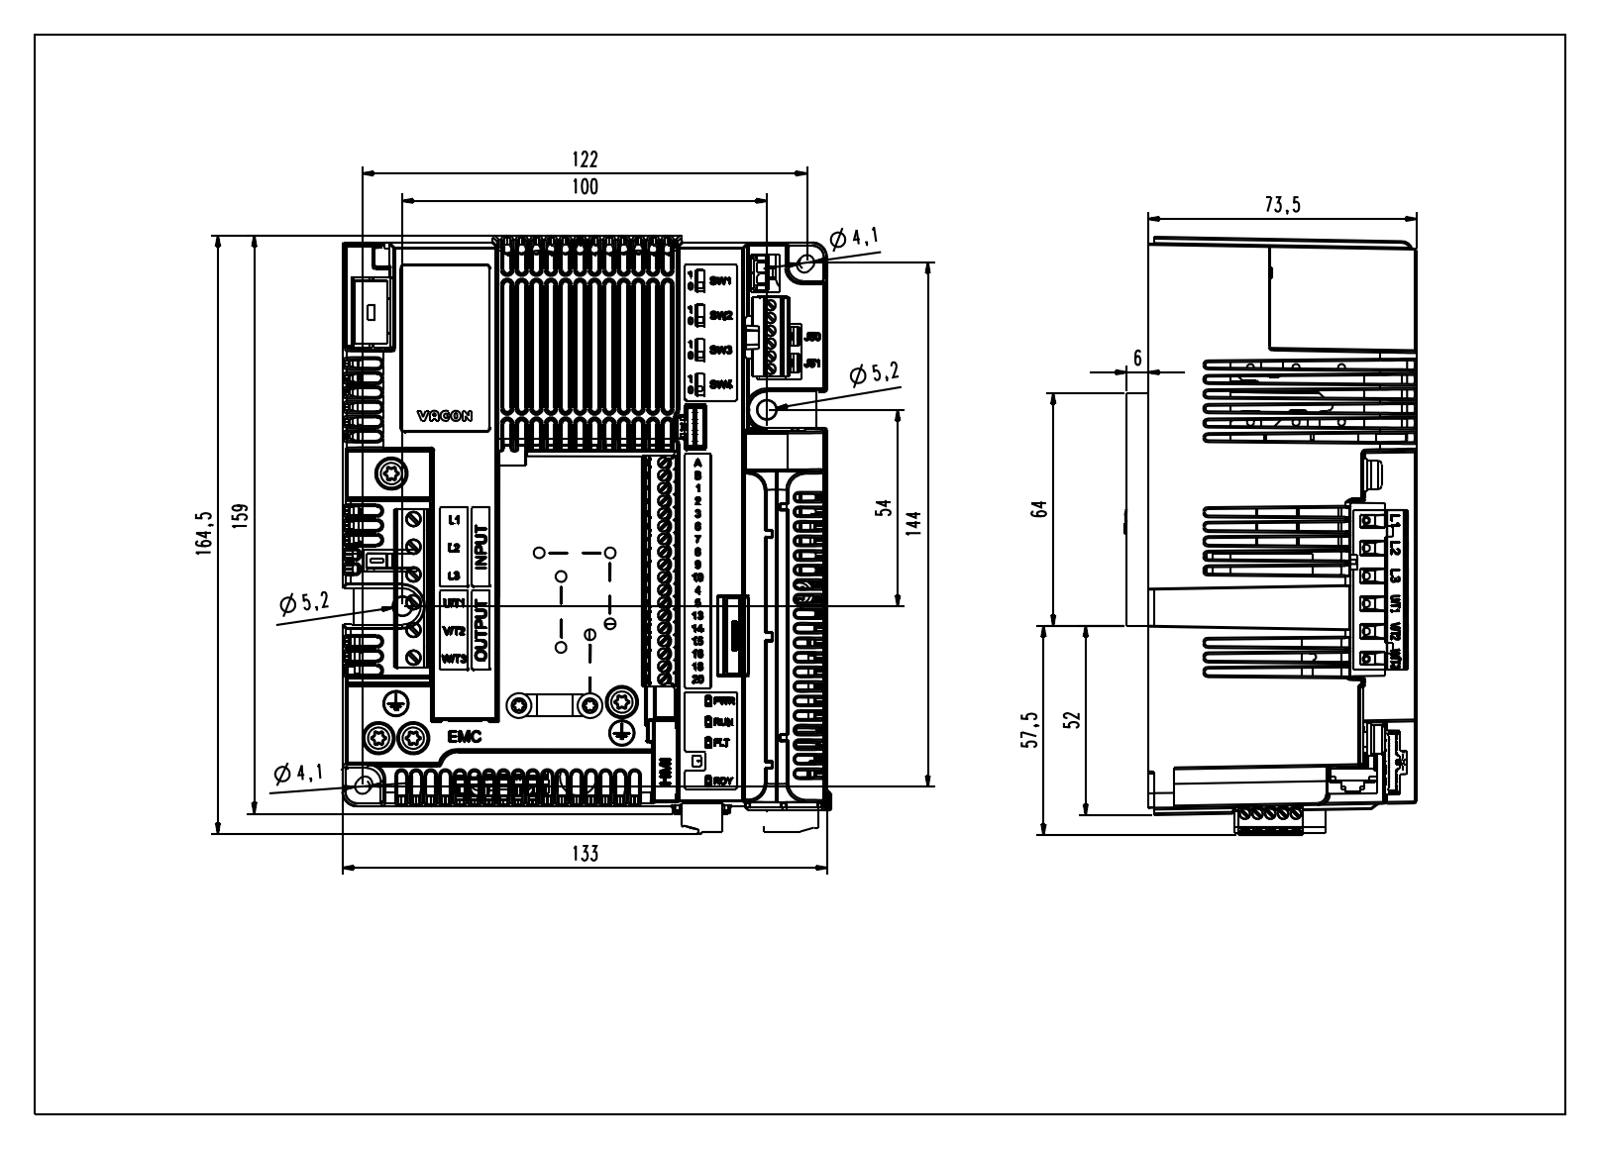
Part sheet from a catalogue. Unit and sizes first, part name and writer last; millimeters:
Units: millimetres
Overall size (bounding box): 164.47 × 134.15 × 79.9
Round holes (diameter × count): ⌀3 ×11, ⌀2.5 ×6, ⌀2.9 ×6, ⌀5 ×6, ⌀4 ×5, ⌀1 ×4, ⌀1.6 ×4, ⌀3.2 ×4, ⌀5.6 ×4, ⌀12 ×4, ⌀6 ×3, ⌀10 ×3
Round bosses / shafts (diameter × count): ⌀0.6 ×24, ⌀2.8 ×6, ⌀8 ×5, ⌀4 ×5, ⌀8.9 ×4, ⌀7.9 ×4, ⌀1.4 ×4, ⌀1 ×4
Partial cylindrical surfaces — rounded edges, fillets, slot ends (radius × count): R0.5 ×560, R0.25 ×476, R0.2 ×104, R0.3 ×65, R0.64 ×52, R1 ×45, R0.63 ×40, R0.1 ×38
Main face-to-face distances: 2.5, 1.5, 7.5, 6, 12, 4, 6.2, 7.7, 0.5, 1
Hole centre spacings: 6.27, 10.6, 38.94, 49.4, 67.42, 68, 84.84, 100.98
Volume: 284 136 mm³ · Surface area: 315 504 mm²
Bodies: 210 solids, 18294 faces (8098 planar, 3233 cylindrical, 6963 other)
Part name (STEP PRODUCT): CAD-3D-VACON20X-MS2; CAD-3D-VACON20X-MS2.sldasm-Part-1_Standard; MSBR1_Standard; CAD-3D-VACON20X-MS2.sldasm-Part-2_Standard (+8 more)
STEP written by: SolidWorks 2007 (CONFIG_CONTROL_DESIGN)
